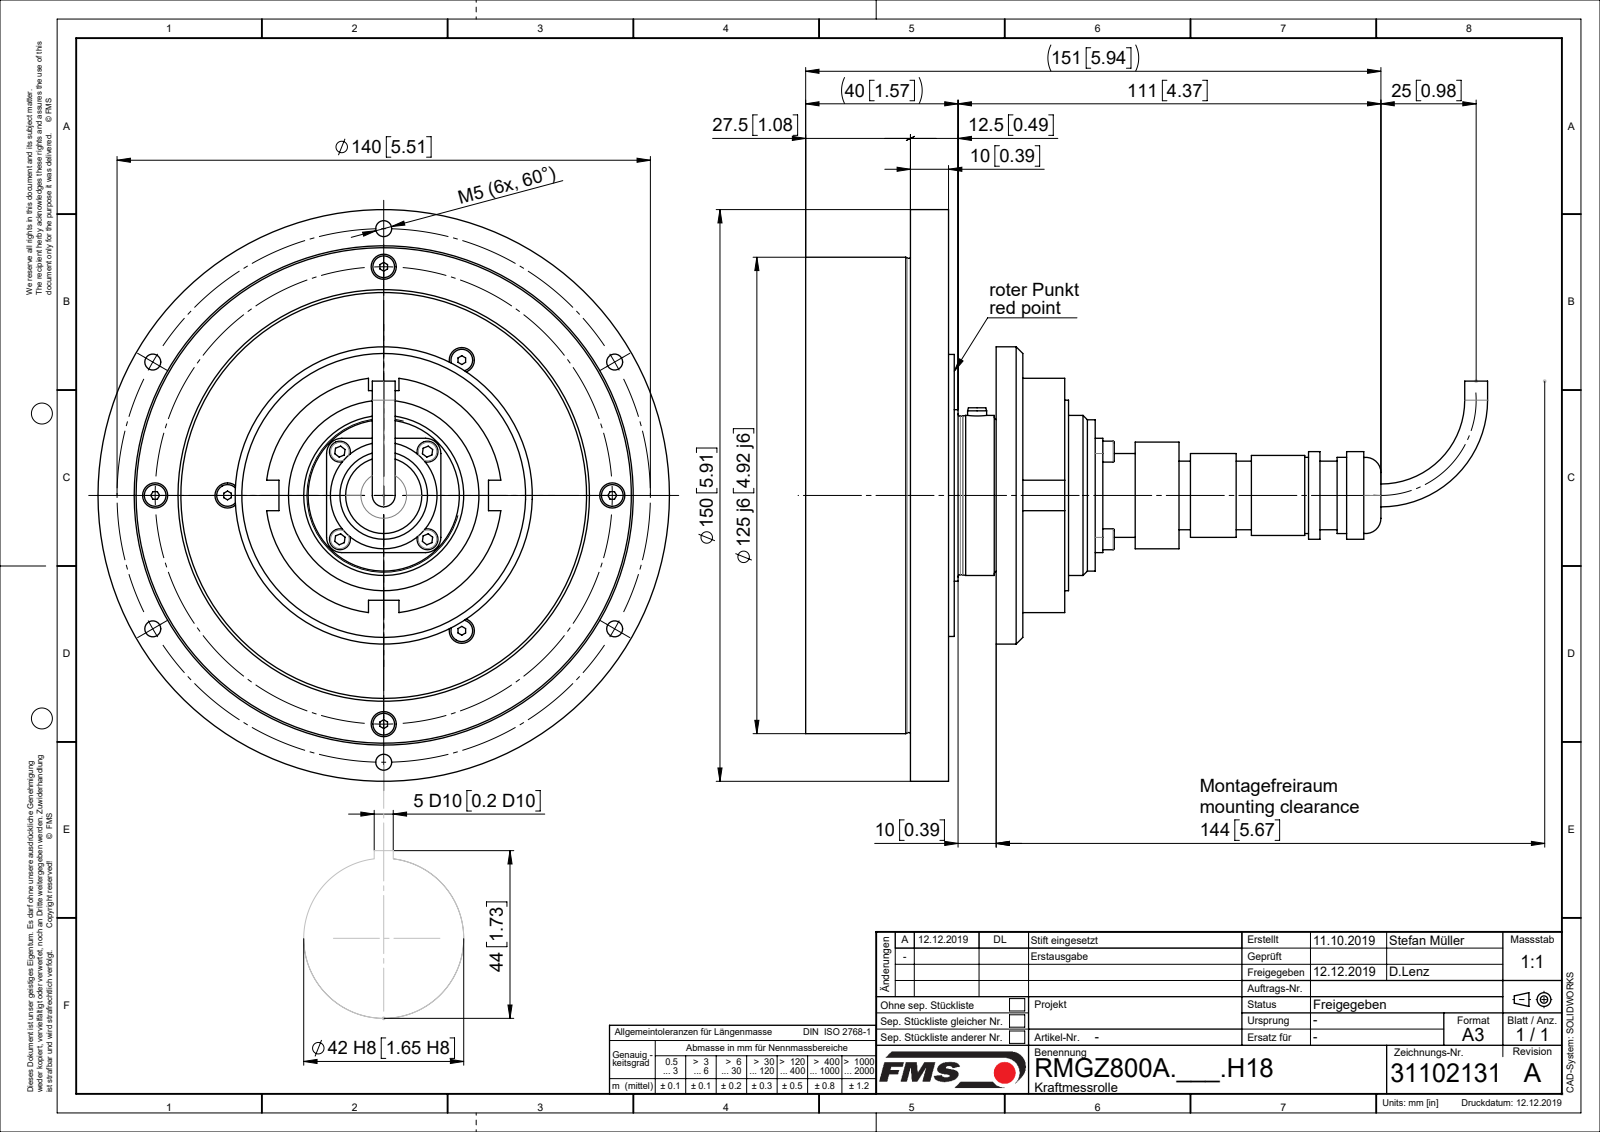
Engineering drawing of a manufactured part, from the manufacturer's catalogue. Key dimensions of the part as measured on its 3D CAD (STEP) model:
Part name (STEP PRODUCT): ZEICHNUNG8; R50563; R4753004; TEIL1 (+8 more)
STEP written by: Mechanical Desktop 2009 (CONFIG_CONTROL_DESIGN)
Units: millimetres
Bodies: 24 solids, 550 faces (158 planar, 250 cylindrical, 142 other)
Overall size (bounding box): 179 × 150 × 150
Volume: 566 851 mm³ · Surface area: 206 899 mm²
Round holes (diameter × count): ⌀2.6 ×11, ⌀3.4 ×7, ⌀4.33 ×6, ⌀16 ×5, ⌀3.2 ×4, ⌀4 ×1, ⌀5 ×1, ⌀6 ×1, ⌀8 ×1, ⌀32.2 ×1, ⌀37.8 ×1, ⌀43 ×1
Round bosses / shafts (diameter × count): ⌀3 ×11, ⌀6 ×8, ⌀5.5 ×4, ⌀2.5 ×4, ⌀150 ×1, ⌀125 ×1, ⌀115 ×1, ⌀106.5 ×1
Partial cylindrical surfaces — rounded edges, fillets, slot ends (radius × count): R4 ×4, R27 ×1, R29 ×1
Main face-to-face distances: 2, 4, 30, 32, 13, 35.5, 37.5, 25.5, 31.5, 29.5
Hole centre spacings: 70, 49.84, 72.42, 121.24, 40.12, 81.12, 16.26, 20.11
